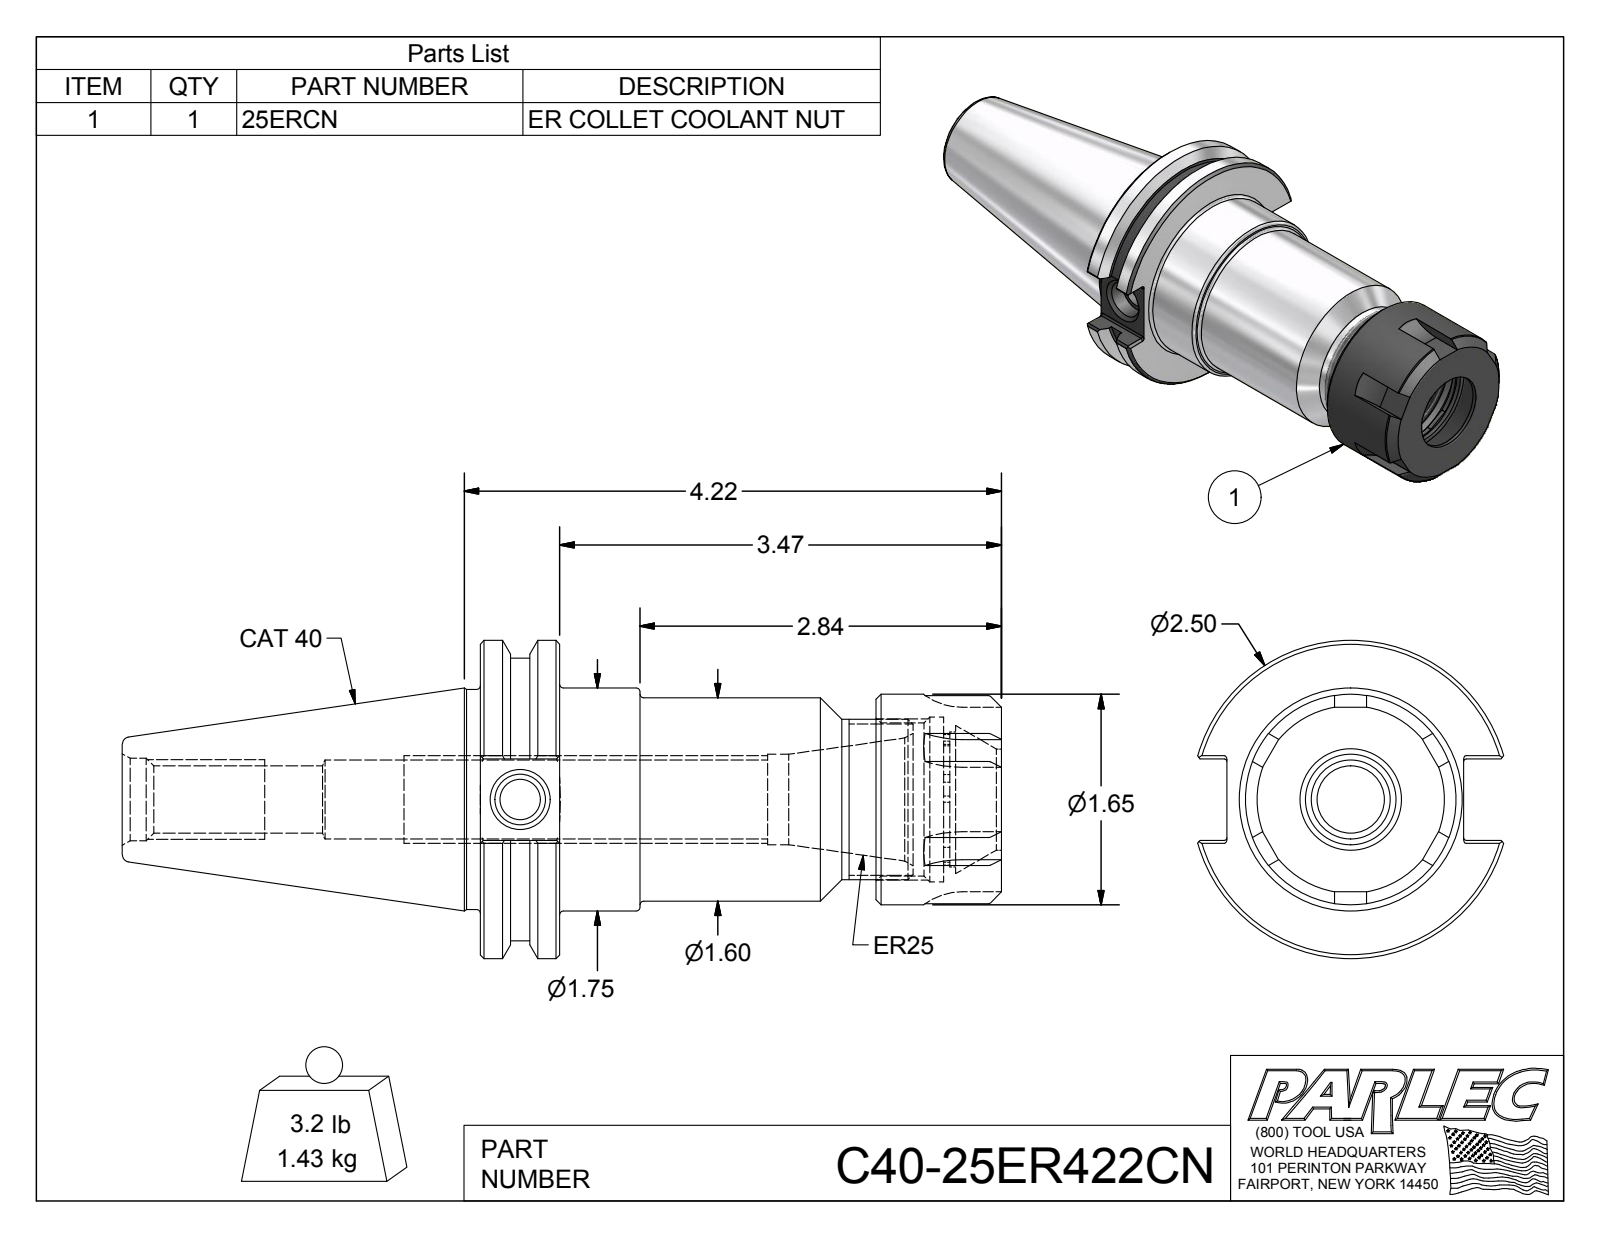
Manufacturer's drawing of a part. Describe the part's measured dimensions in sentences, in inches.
The part is named "C40-25ER422CN; C40-25ER4-1; 25ERCN". Its 3-D file was written by "Autodesk Inventor 2012 (AUTOMOTIVE_DESIGN)". It is 2 solids with 145 faces: 61 planar, 44 cylindrical and 40 other. Overall it measures 6.908 by 2.5 by 2.403 inches. Its volume is 11.21 cubic inches and its surface area 62.52 square inches. Round holes: 1 of diameter 0.315, 1 of diameter 0.399, 1 of diameter 0.527, 1 of diameter 0.62, 1 of diameter 0.648, 1 of diameter 0.71, 1 of diameter 0.794, 1 of diameter 1.057, 1 of diameter 1.201, 1 of diameter 1.294. Round bosses or shafts: 1 of diameter 2.5, 1 of diameter 2.219, 1 of diameter 1.75, 1 of diameter 1.73, 1 of diameter 1.654, 1 of diameter 1.595, 1 of diameter 1.26. Partial cylindrical surfaces (rounded edges, fillets, slot ends): 12 of radius 0.02, 6 of radius 0.5, 1 of radius 0.472, 1 of radius 0.515. The main face-to-face distances are 0.625, 4.095, 3.47, 3.111, 2.486, 0.984, 3.642, 3.017, 0.531, 0.453.
